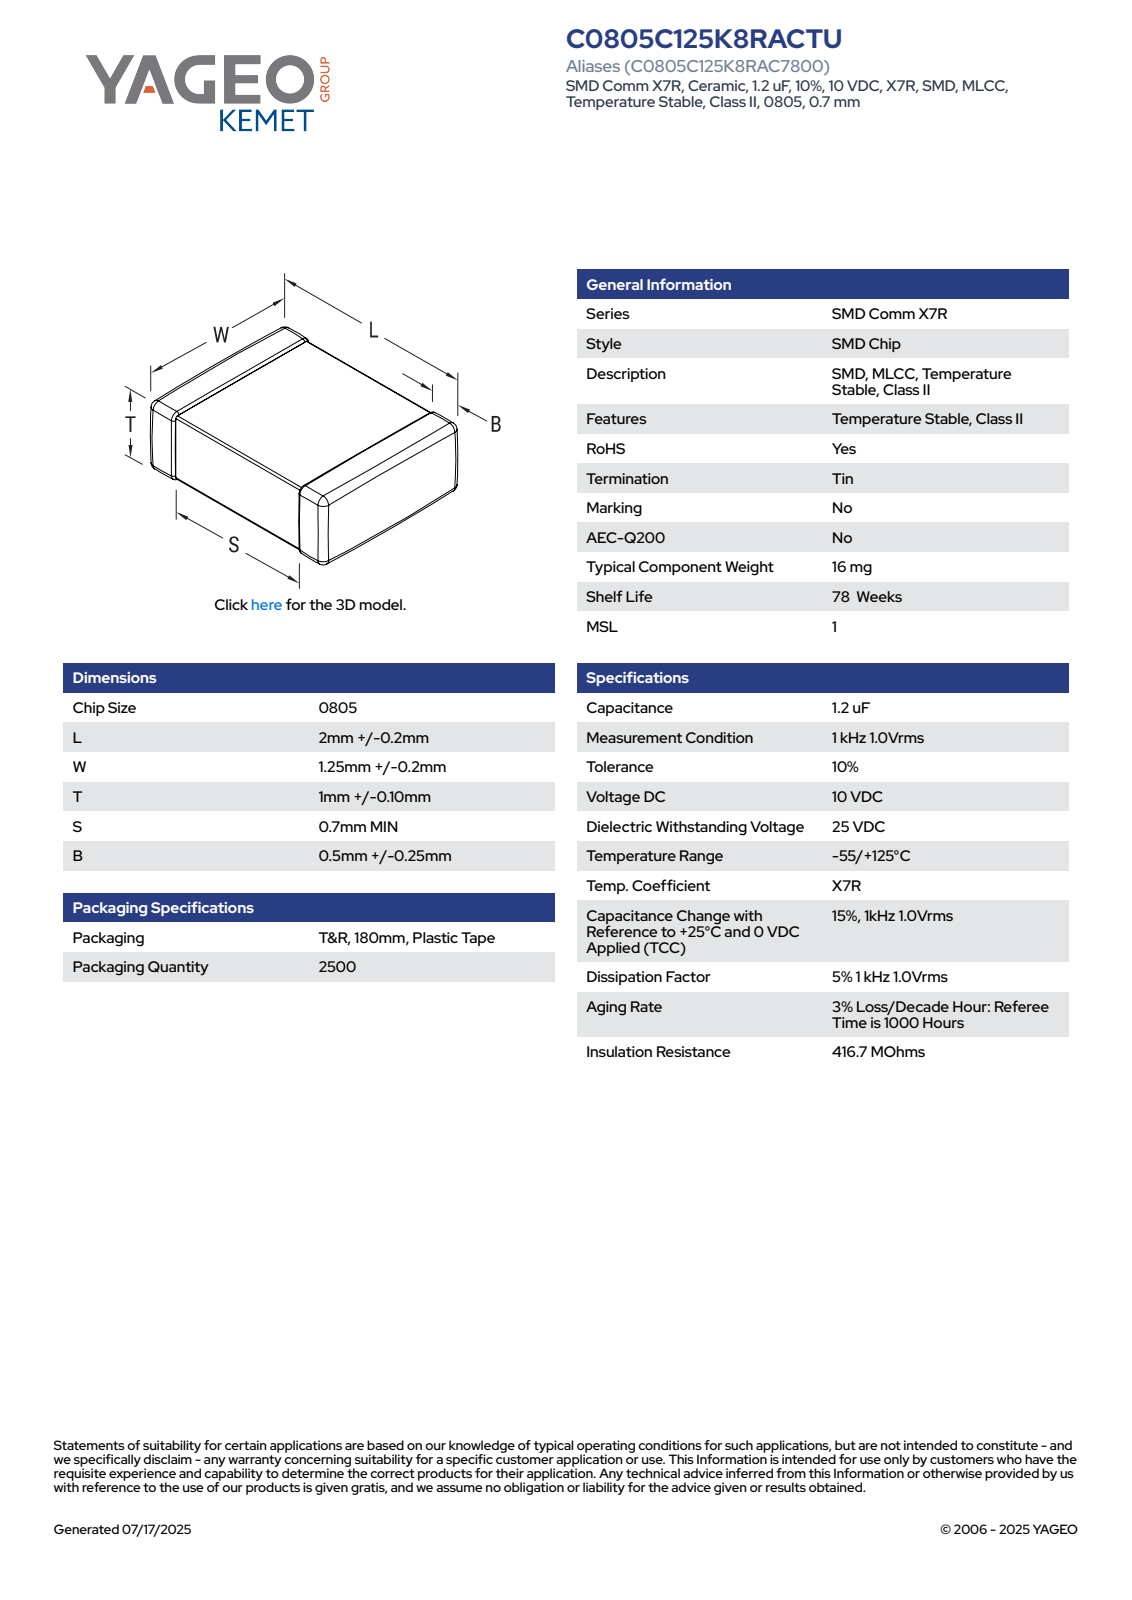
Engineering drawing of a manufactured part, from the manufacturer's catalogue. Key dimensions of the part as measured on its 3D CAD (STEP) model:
Part name (STEP PRODUCT): CCS_CCSTD_0805_L2.2W1.45T1.1B0.5
STEP written by: SolidWorks 2014 (AUTOMOTIVE_DESIGN)
Units: millimetres
Bodies: 4 solids, 121 faces (71 planar, 34 cylindrical, 16 other)
Overall size (bounding box): 2.2 × 1.45 × 1.1
Volume: 3 mm³ · Surface area: 14 mm²
Main face-to-face distances: 1.07, 1.42, 1.04, 2.2, 1.1, 1.39, 1.45, 0.97, 1.23, 1.19
